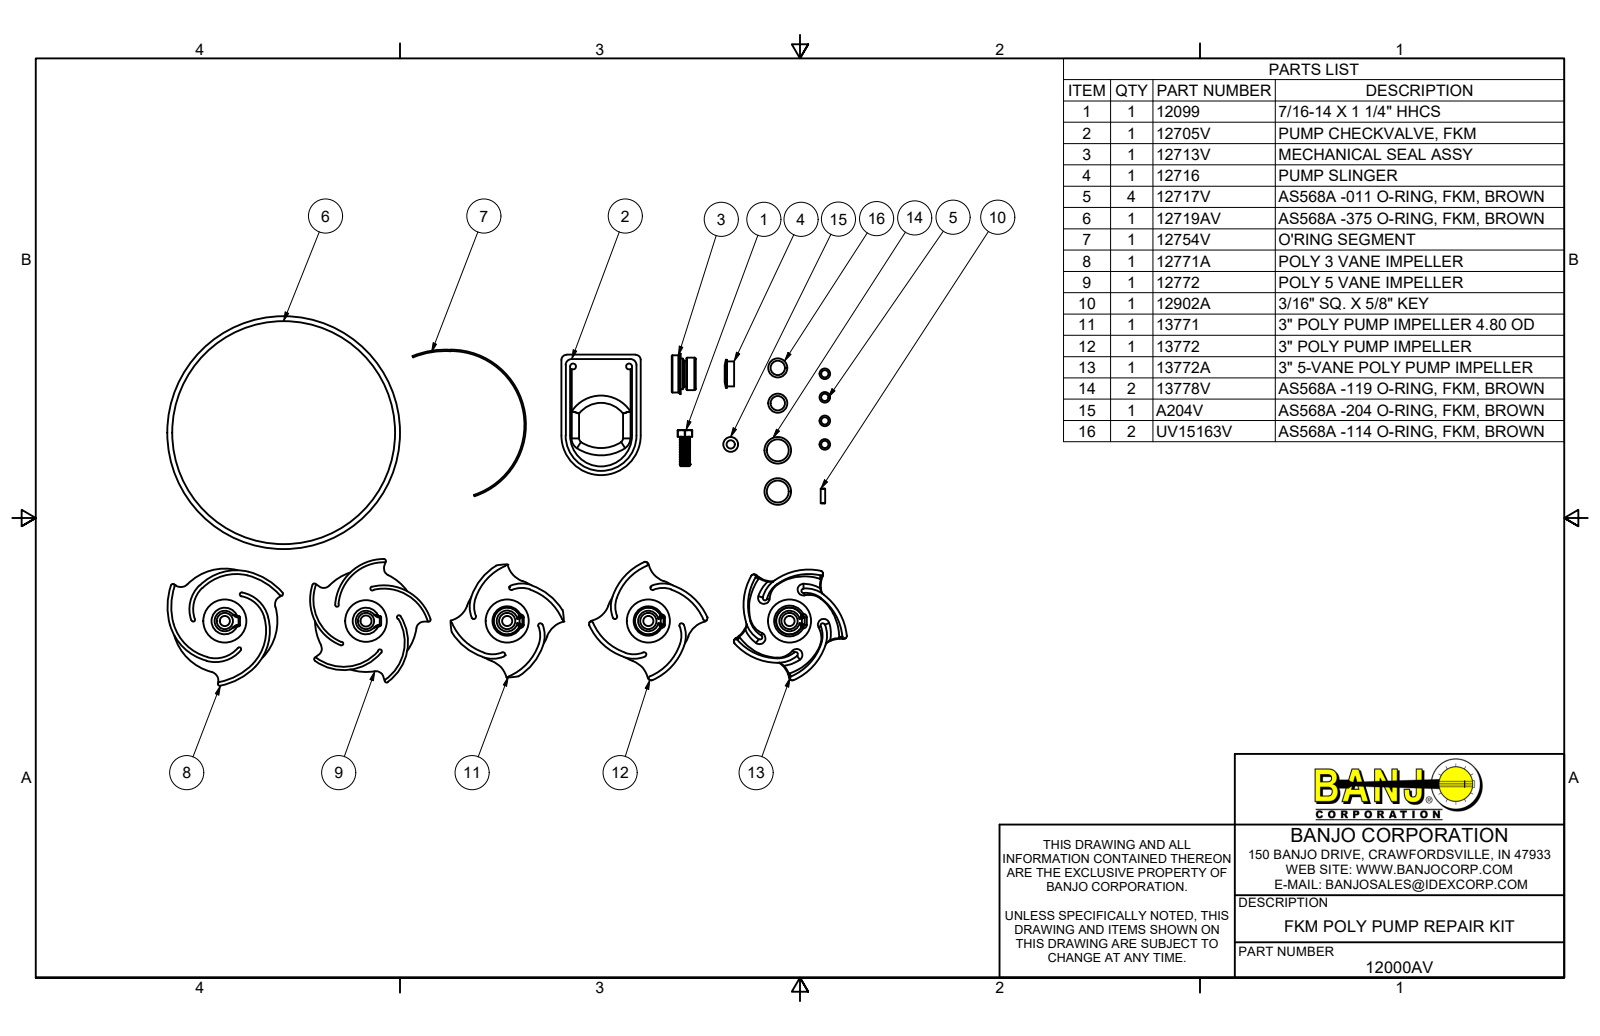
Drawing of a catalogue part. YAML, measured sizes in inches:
part_name: "12000AV; 12772; 12099; 12705V (+8 more)"
step_written_by: "Autodesk Inventor 2019 (AUTOMOTIVE_DESIGN)"
units: inches
bodies: {solids: 15, faces: 638, planar: 210, cylindrical: 166, other: 262}
overall_size: [20.522, 9.895, 2.091]
volume: 13.94
surface_area: 162.8
round_holes:
  - {diameter: 0.25, count: 2}
  - {diameter: 0.437, count: 1}
  - {diameter: 0.685, count: 1}
  - {diameter: 0.719, count: 1}
  - {diameter: 0.75, count: 1}
  - {diameter: 0.752, count: 1}
  - {diameter: 0.813, count: 1}
  - {diameter: 0.875, count: 1}
  - {diameter: 0.98, count: 1}
  - {diameter: 1, count: 1}
  - {diameter: 1.375, count: 1}
round_bosses_or_shafts:
  - {diameter: 0.379, count: 17}
  - {diameter: 1.75, count: 1}
  - {diameter: 1.72, count: 1}
  - {diameter: 1.575, count: 1}
  - {diameter: 1.375, count: 1}
  - {diameter: 1.313, count: 1}
  - {diameter: 1.305, count: 1}
  - {diameter: 1.19, count: 1}
partial_cylinders:
  - {radius: 0.008, count: 26}
  - {radius: 0.015, count: 13}
  - {radius: 0.08, count: 10}
  - {radius: 0.06, count: 7}
  - {radius: 0.5, count: 7}
  - {radius: 1.926, count: 5}
  - {radius: 2.086, count: 5}
  - {radius: 0.03, count: 2}
face_to_face_distances: [0.187, 0.375, 0.563, 0.25, 0.063, 0.625, 3.187, 0.628, 0.815, 1.19]
hole_center_spacings: [2.375, 3.889, 4.608, 5.137, 5.984, 6.635, 8.65, 9.667]
